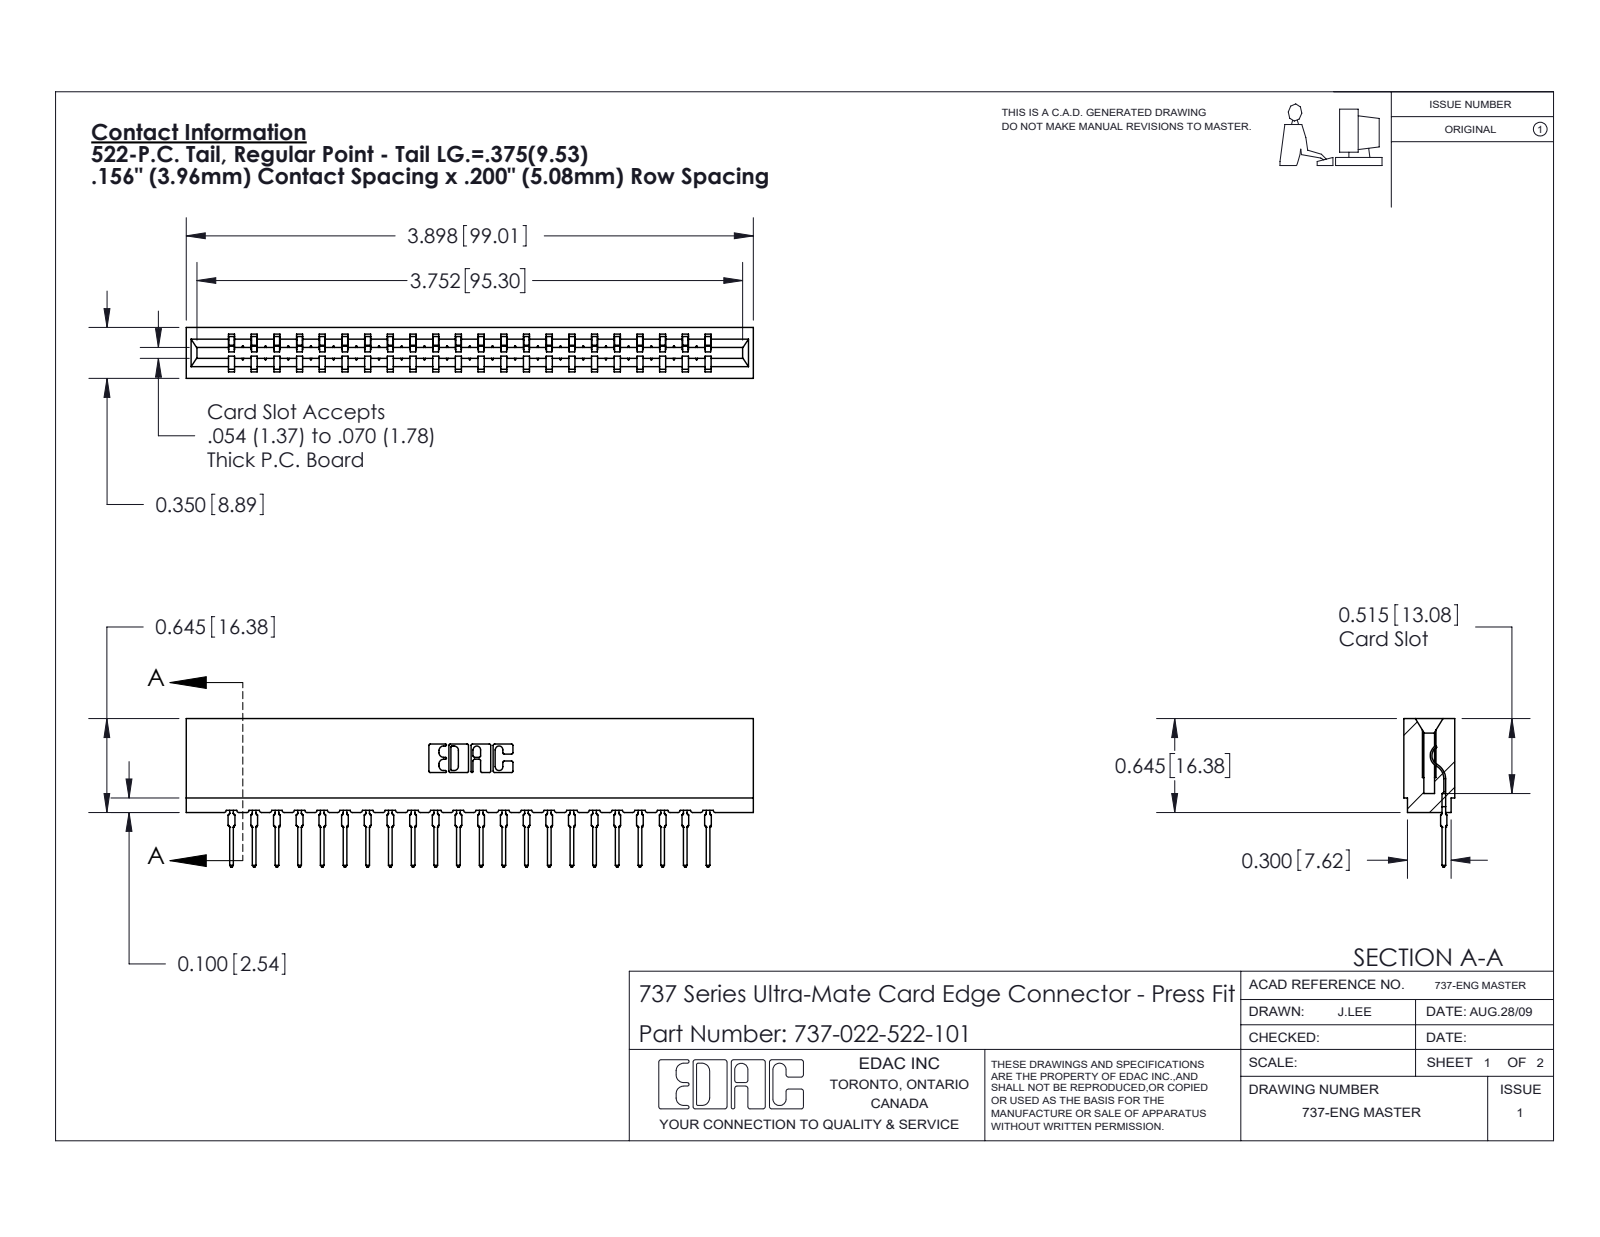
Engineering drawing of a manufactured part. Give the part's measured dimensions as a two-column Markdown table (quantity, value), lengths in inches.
| quantity | value |
| --- | --- |
| part name | 737 Part_Insulator Option - 01; 745-292-001_522; 737-022-522-101 |
| STEP written by | SolidWorks 2020 (CONFIG_CONTROL_DESIGN) |
| units | inches |
| bodies | 23 solids, 2580 faces (1550 planar, 458 cylindrical, 572 other) |
| overall size | 3.898 × 1.021 × 0.35 |
| volume | 0.593 in³ |
| surface area | 19.76 in² |
| partial cylindrical surfaces (radius × count) | 0.015 × 44, 0.021 × 44, 0.01 × 22, 0.007 × 6, 0.031 × 6, 0.005 × 4, 0.011 × 4, 0.026 × 3 |
| main face-to-face distances | 0.138, 0.212, 0.35, 0.156, 0.074, 0.624, 0.78, 1.248, 1.404, 0.468 |
